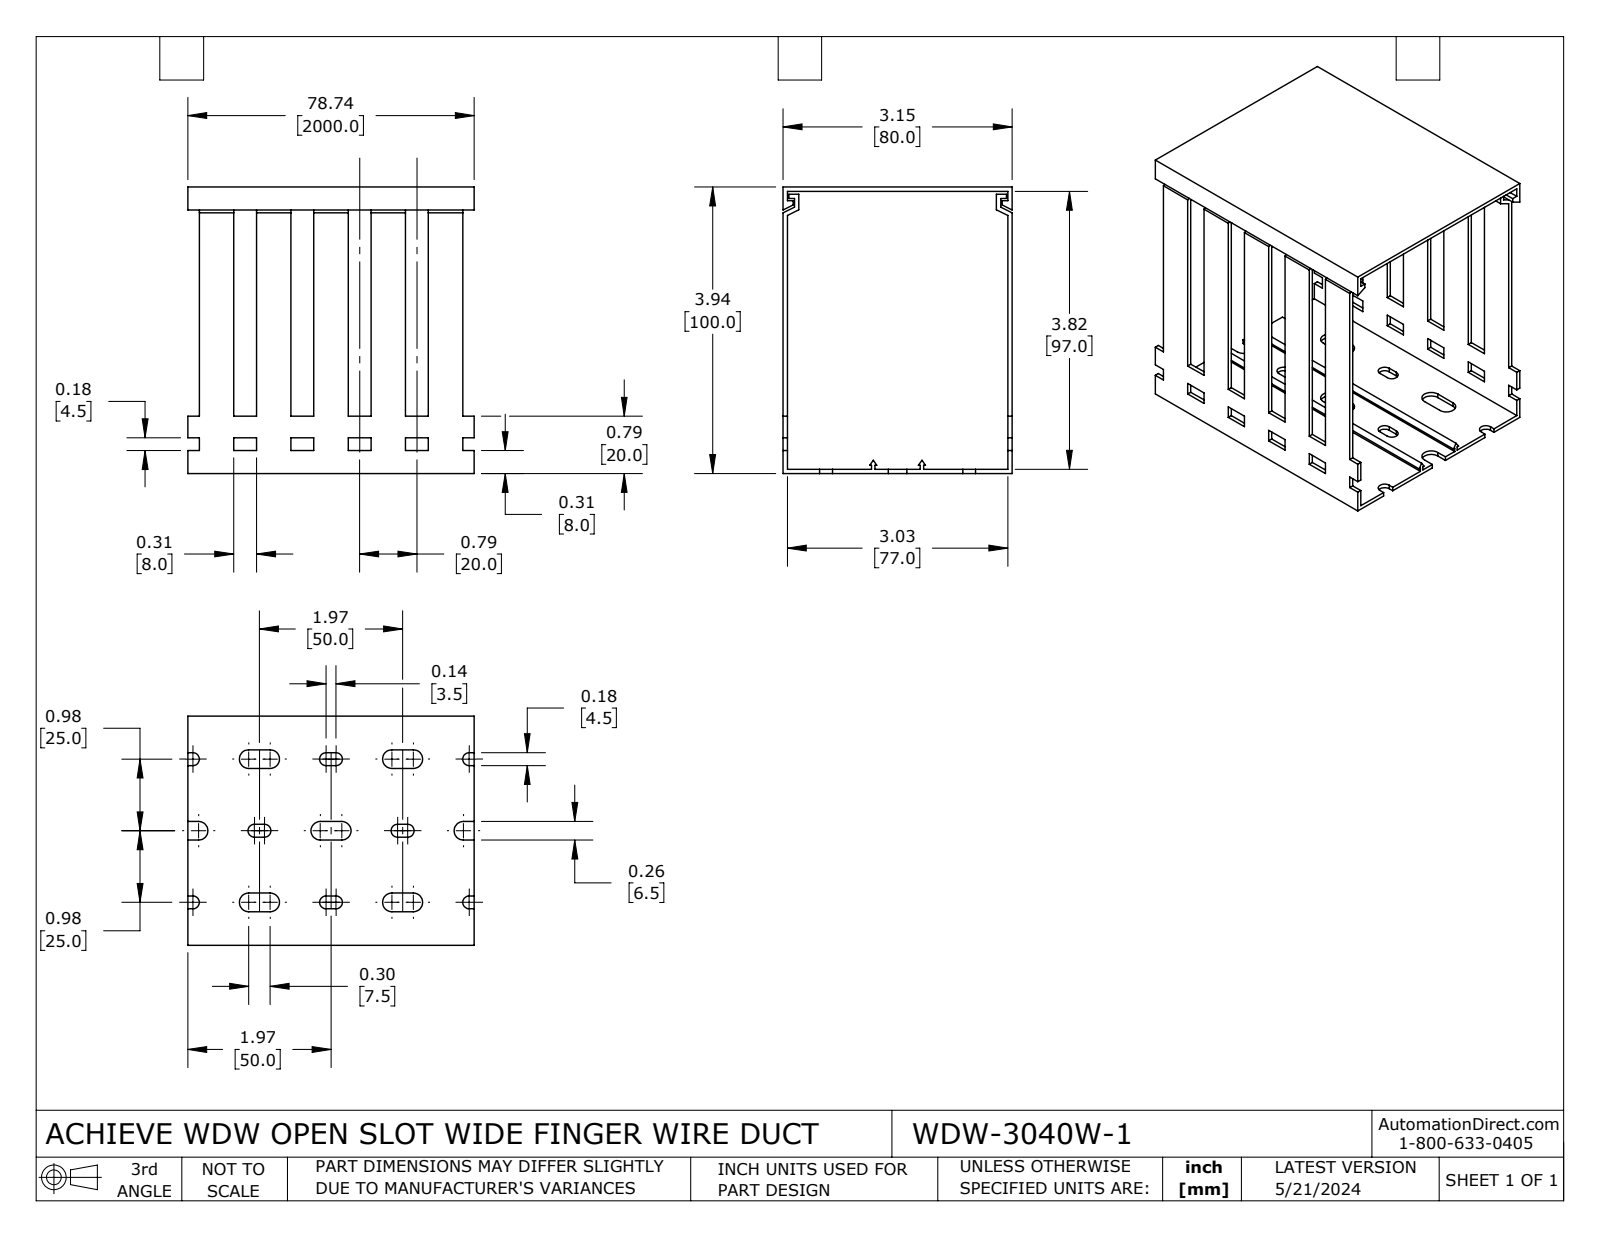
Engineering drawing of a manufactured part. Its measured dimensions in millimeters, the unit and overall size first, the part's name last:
Units: millimetres
Overall size (bounding box): 100 × 100 × 80
Partial cylindrical surfaces — rounded edges, fillets, slot ends (radius × count): R2.25 ×12, R3.25 ×12
Main face-to-face distances: 1.5, 98.5, 78.5, 100, 80, 97, 77, 20, 4, 40
Volume: 46 151 mm³ · Surface area: 66 082 mm²
Bodies: 2 solids, 258 faces (222 planar, 36 cylindrical, 0 other)
Part name (STEP PRODUCT): WDW-3040W-1
STEP written by: SolidWorks 2023 (CONFIG_CONTROL_DESIGN)
